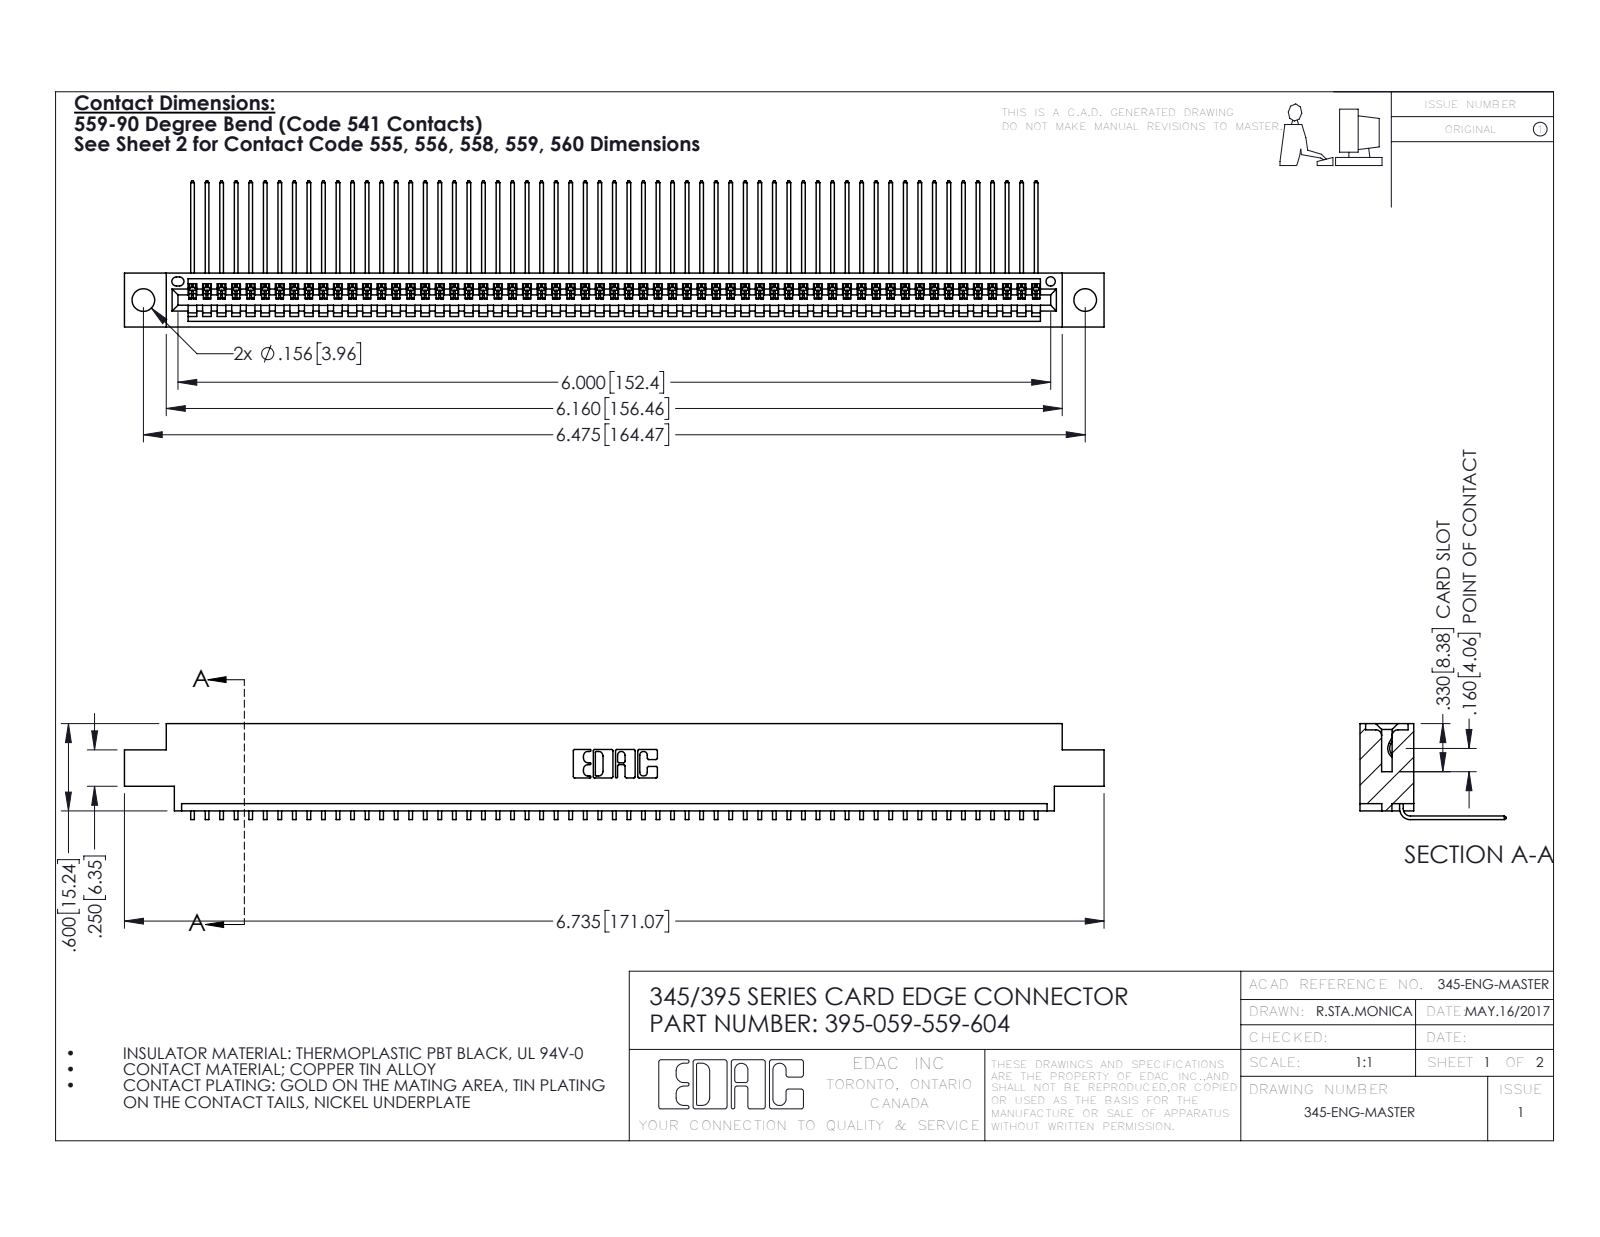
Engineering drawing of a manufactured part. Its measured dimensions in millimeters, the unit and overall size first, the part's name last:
Units: millimetres
Overall size (bounding box): 171.1 × 25.5 × 16.7
Round holes (diameter × count): ⌀4 ×2, ⌀1.6 ×1
Partial cylindrical surfaces — rounded edges, fillets, slot ends (radius × count): R0.2 ×118, R0.3 ×22, R0.2 ×6, R0.8 ×6, R0.7 ×3, R0.8 ×2, R1 ×2, R0.4 ×1
Main face-to-face distances: 1.8, 7.6, 9.4, 5.1, 2.5, 6.9, 0.6, 5.7, 4.4, 3.8
Hole centre spacings: 6.9, 158.5, 164.5
Volume: 16 390 mm³ · Surface area: 23 090 mm²
Bodies: 60 solids, 3670 faces (2562 planar, 1108 cylindrical, 0 other)
Part name (STEP PRODUCT): 345-292-001_558 559 Tail - 1; 395-059-559-604; 345 Part_0.170 Offset - 0.156 Dia-TH
STEP written by: SolidWorks 2016 (CONFIG_CONTROL_DESIGN)
